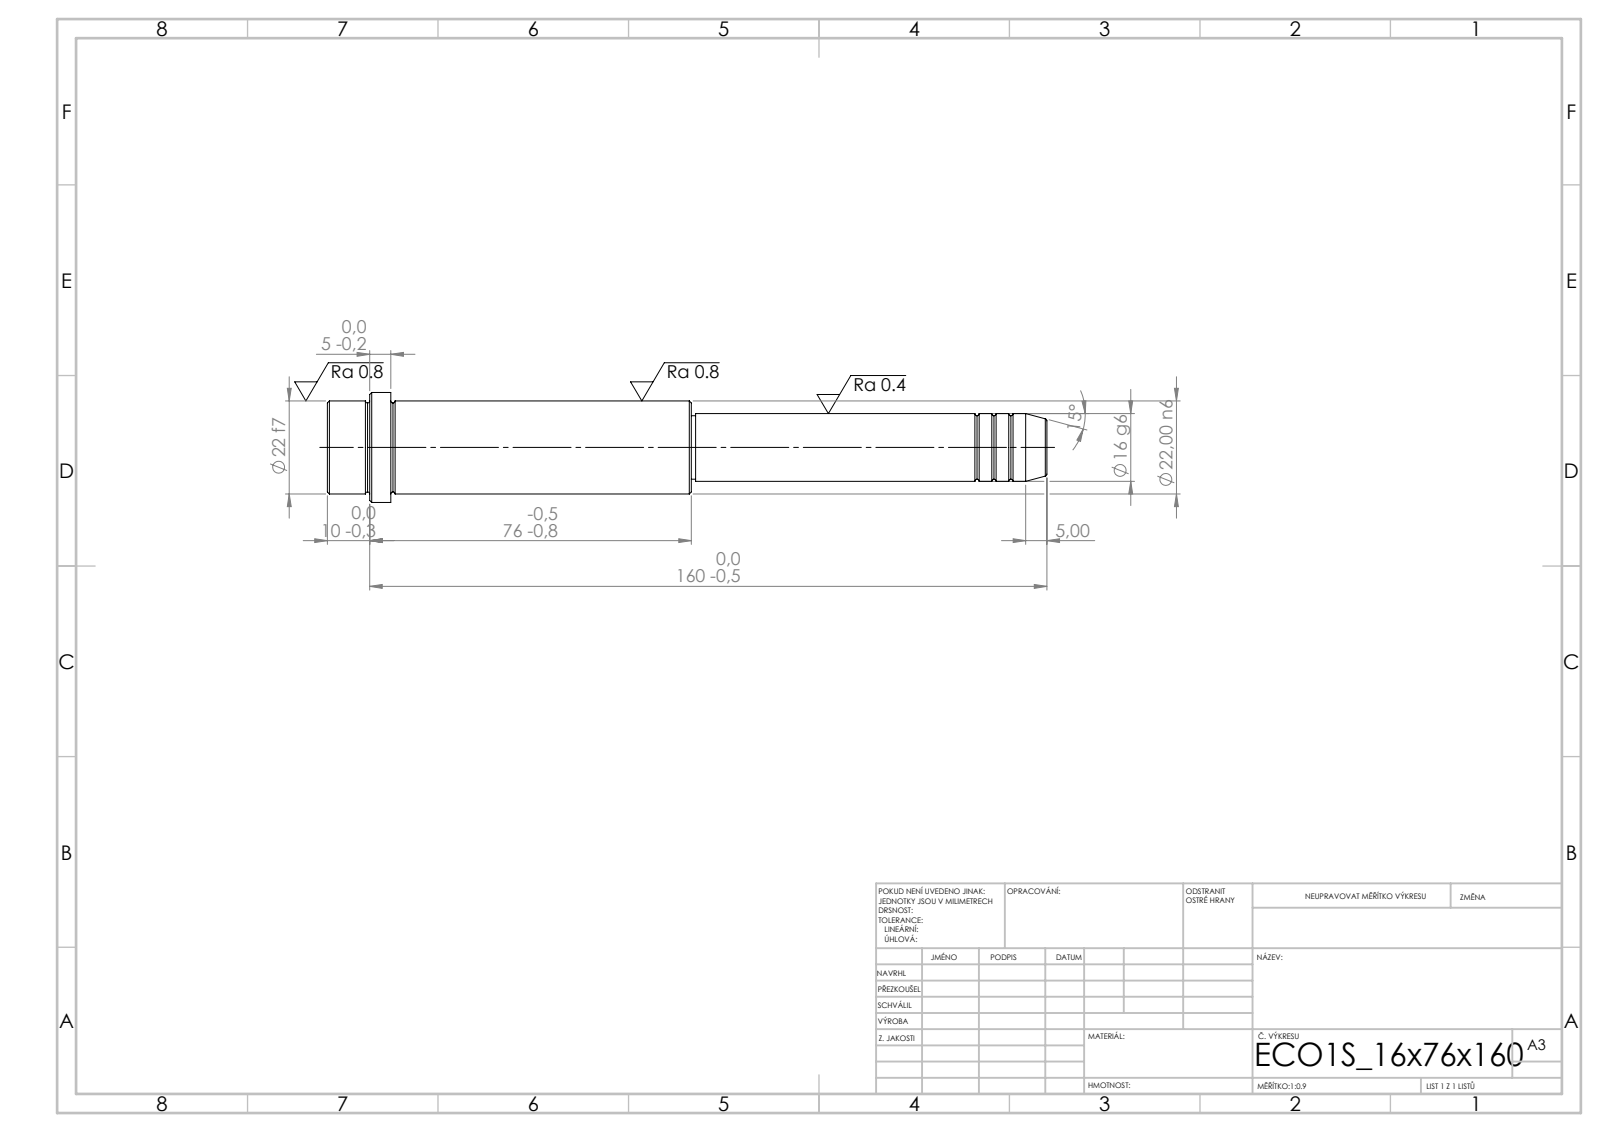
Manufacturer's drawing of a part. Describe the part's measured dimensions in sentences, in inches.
Its 3-D file was written by "SolidWorks 2019 (CONFIG_CONTROL_DESIGN)". It is 1 solid with 52 faces: 6 planar, 16 cylindrical and 30 other. Overall it measures 6.693 by 1.024 by 1.024 inches. Its volume is 3.052 cubic inches and its surface area 17.58 square inches. Round bosses or shafts: 1 of diameter 1.024, 1 of diameter 0.866, 1 of diameter 0.63, 1 of diameter 0.591. The main face-to-face distances are 3.386, 2.795, 0.591, 3.307, 6.102, 6.693, 6.299, 2.992, 0.197, 0.394.
